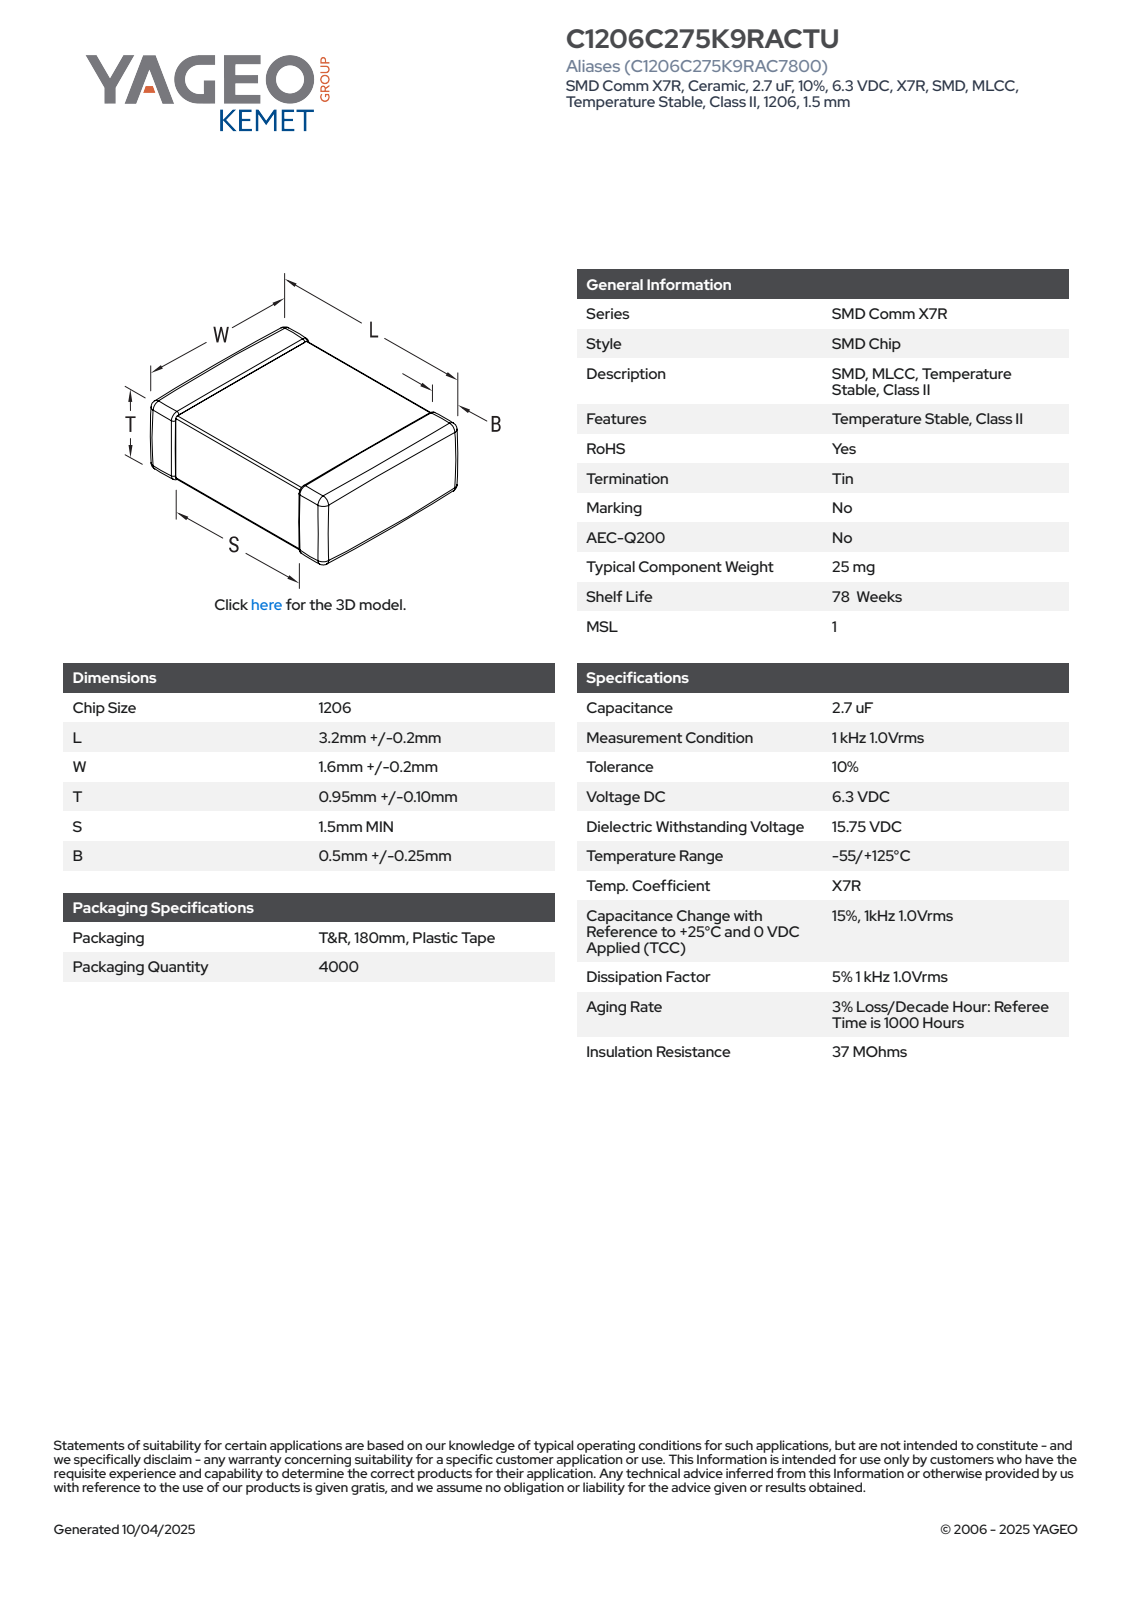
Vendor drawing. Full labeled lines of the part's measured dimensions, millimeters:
Part name (STEP PRODUCT): CCS_CCSTD_1206_L3.4W1.8T1.05B0.5
STEP written by: SolidWorks 2021 (AUTOMOTIVE_DESIGN)
Units: millimetres
Bodies: 4 solids, 125 faces (71 planar, 38 cylindrical, 16 other)
Overall size (bounding box): 3.4 × 1.8 × 1.05
Volume: 6 mm³ · Surface area: 23 mm²
Main face-to-face distances: 1.01, 0.97, 1.76, 1.05, 1.72, 3.4, 1.8, 1.02, 0.98, 1.57
